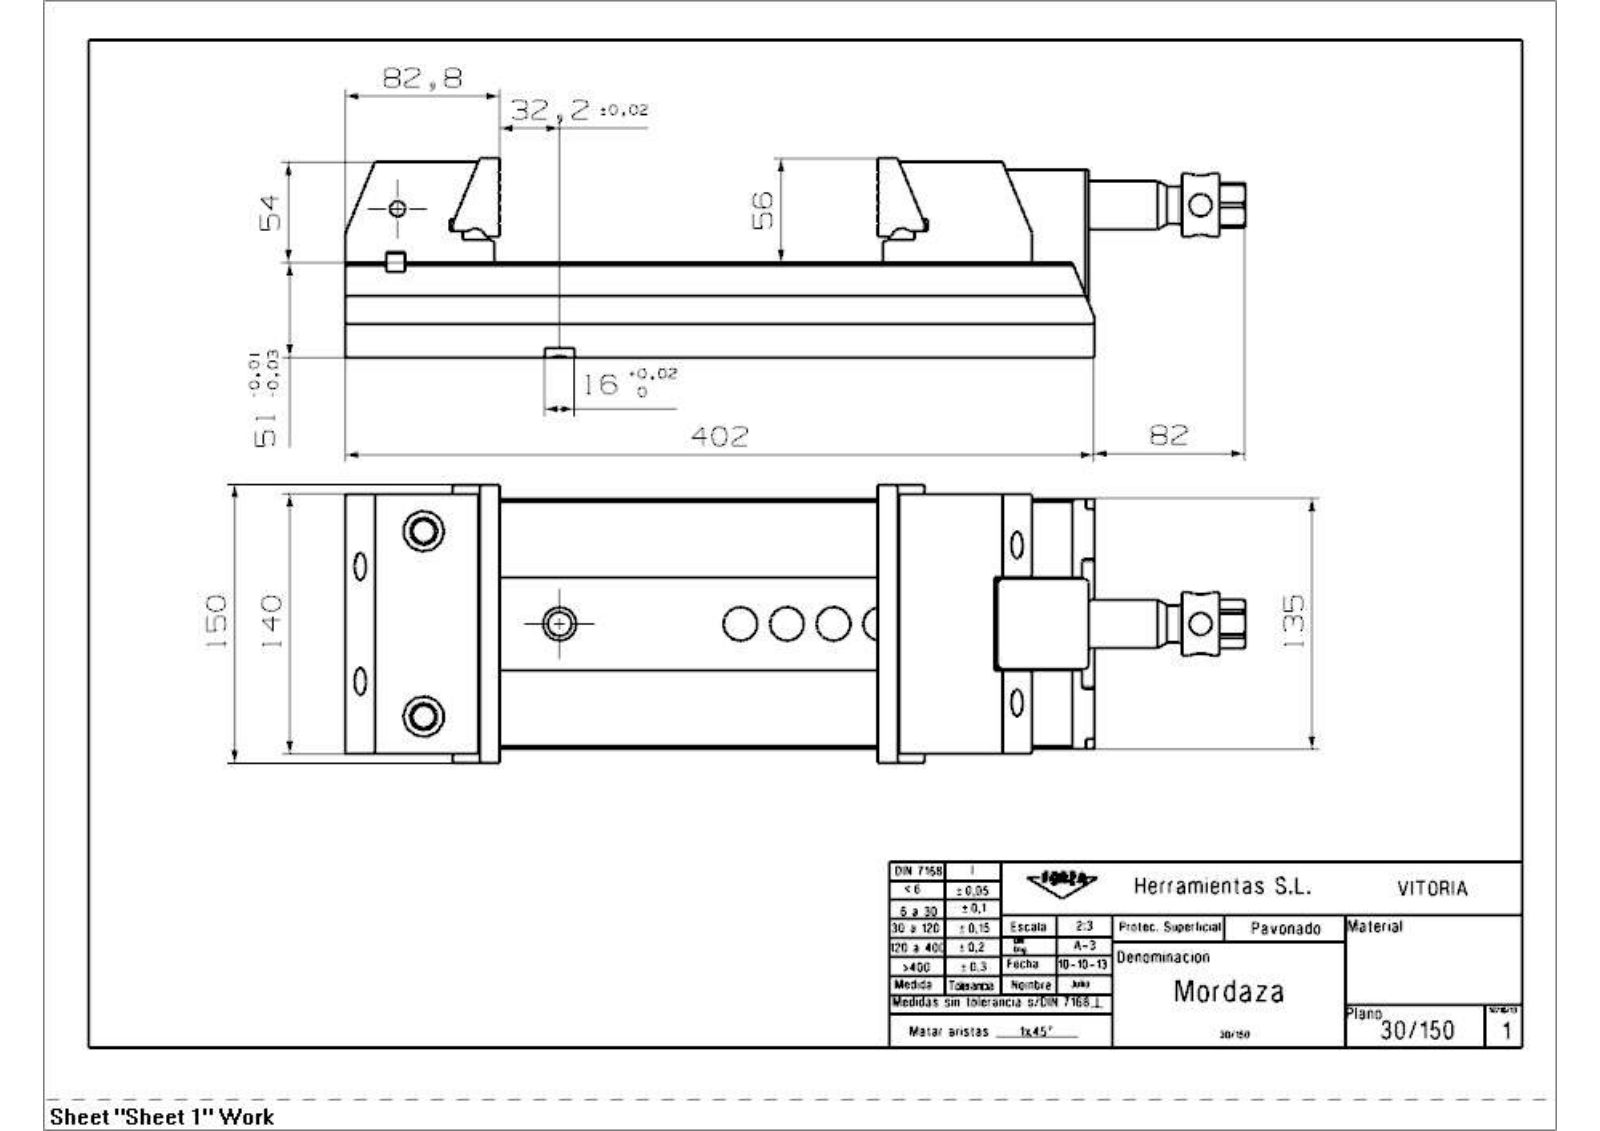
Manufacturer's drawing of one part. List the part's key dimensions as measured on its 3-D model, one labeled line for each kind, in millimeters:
Part name (STEP PRODUCT): 30_150_Mordaza
STEP written by: SIEMENS PLM Software NX 7.5 (AUTOMOTIVE_DESIGN)
Units: millimetres
Bodies: 15 solids, 493 faces (306 planar, 117 cylindrical, 70 other)
Overall size (bounding box): 490 × 150 × 108.4
Volume: 3 391 000 mm³ · Surface area: 490 394 mm²
Round holes (diameter × count): ⌀13 ×6, ⌀15 ×6, ⌀5.19 ×5, ⌀6.99 ×4, ⌀8.5 ×4, ⌀8.78 ×4, ⌀10 ×4, ⌀10.58 ×4, ⌀19 ×4, ⌀12 ×2, ⌀12.38 ×2, ⌀18 ×2
Round bosses / shafts (diameter × count): ⌀34 ×1, ⌀33.8 ×1, ⌀26 ×1, ⌀20 ×1, ⌀16.5 ×1
Partial cylindrical surfaces — rounded edges, fillets, slot ends (radius × count): R1.5 ×4, R8 ×4, R20 ×4, R1.6 ×2, R5.5 ×2, R6 ×2, R4 ×1, R9 ×1
Main face-to-face distances: 51.8, 86.5, 32.1, 19.7, 5.5, 43, 27, 92, 106.2, 54.4
Hole centre spacings: 11.5, 73.5, 62, 85, 95.18, 11.61, 11.66, 22.27
